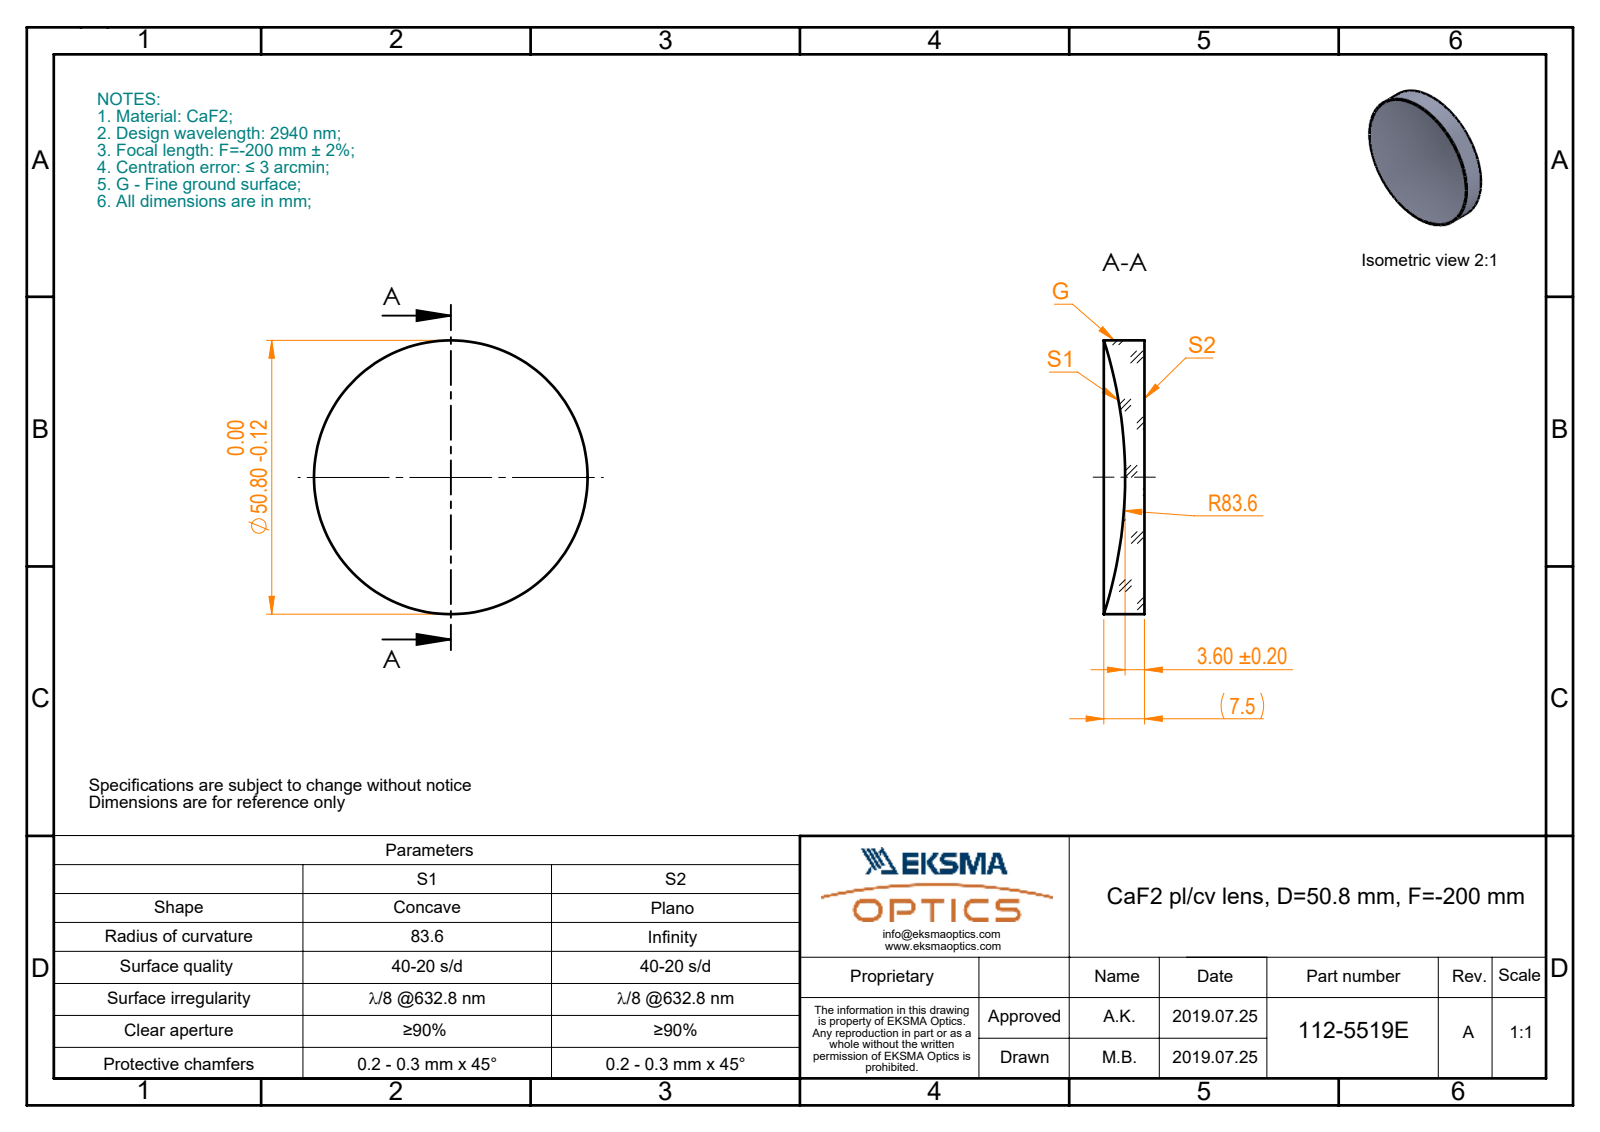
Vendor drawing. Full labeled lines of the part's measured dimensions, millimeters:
Part name (STEP PRODUCT): 112-5519E CaF2 pl-cv 50.8 F-200
STEP written by: SolidWorks 2017 (CONFIG_CONTROL_DESIGN)
Units: millimetres
Bodies: 1 solid, 5 faces (1 planar, 2 cylindrical, 2 other)
Overall size (bounding box): 50.8 × 50.8 × 7.55
Volume: 11 267 mm³ · Surface area: 5 308 mm²
Round bosses / shafts (diameter × count): ⌀50.8 ×1
